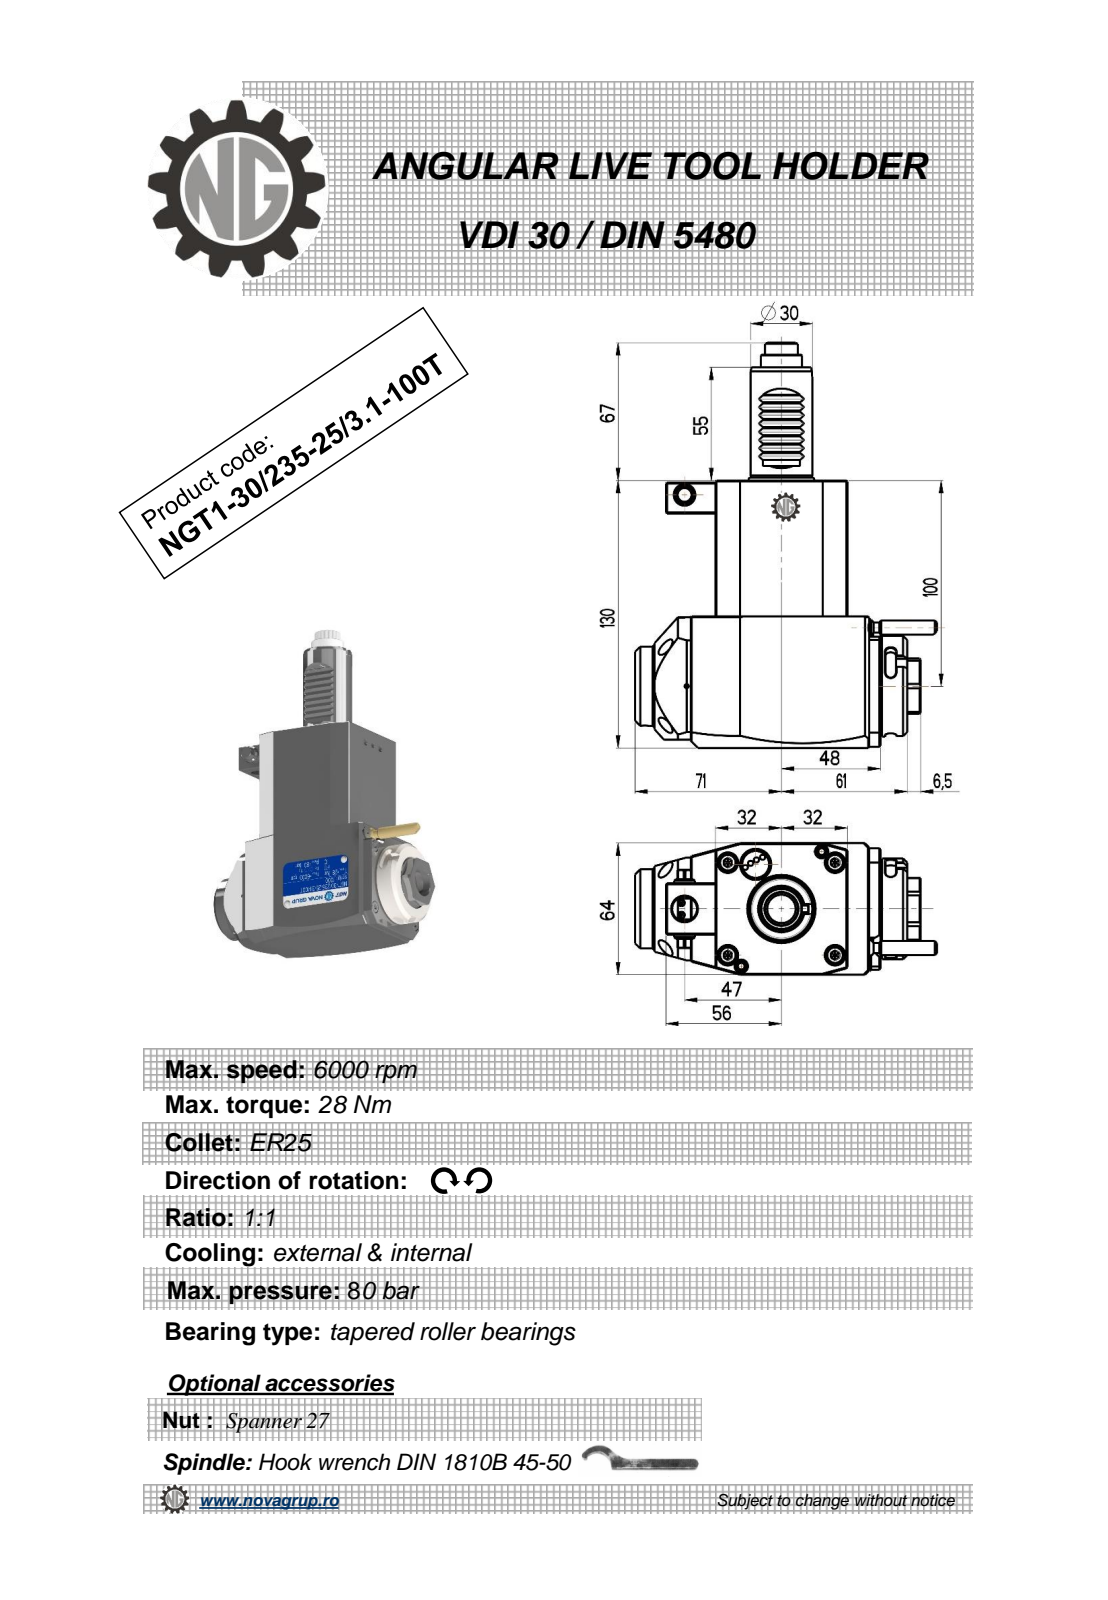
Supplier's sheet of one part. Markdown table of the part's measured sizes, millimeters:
| quantity | value |
| --- | --- |
| part name | NGT1_30_235_25_3_1_100T |
| STEP written by | PRO/ENGINEER BY PARAMETRIC TECHNOLOGY CORPORATION, 2010280 (CONFIG_CONTROL_DESIGN) |
| units | millimeters |
| bodies | 1 solid, 433 faces (188 planar, 155 cylindrical, 90 other) |
| overall size | 197 × 146.38 × 64 |
| volume | 750 794 mm³ |
| surface area | 62 908 mm² |
| round holes (diameter × count) | 2.5 × 1, 3 × 1, 9.5 × 1, 12 × 1, 18 × 1 |
| round bosses / shafts (diameter × count) | 8 × 2, 49 × 1, 42 × 1, 38.5 × 1, 30 × 1, 20 × 1, 10 × 1, 7 × 1 |
| partial cylindrical surfaces (radius × count) | 1.98 × 36, 0.3 × 8, 2.5 × 6, 180 × 2, 3.85 × 1, 4.25 × 1, 4.5 × 1, 7.08 × 1 |
| main face-to-face distances | 64, 130, 16, 80, 72.18, 13, 66, 93, 29, 39 |
| hole center spacings | 34.25, 65.8, 91.5 |
